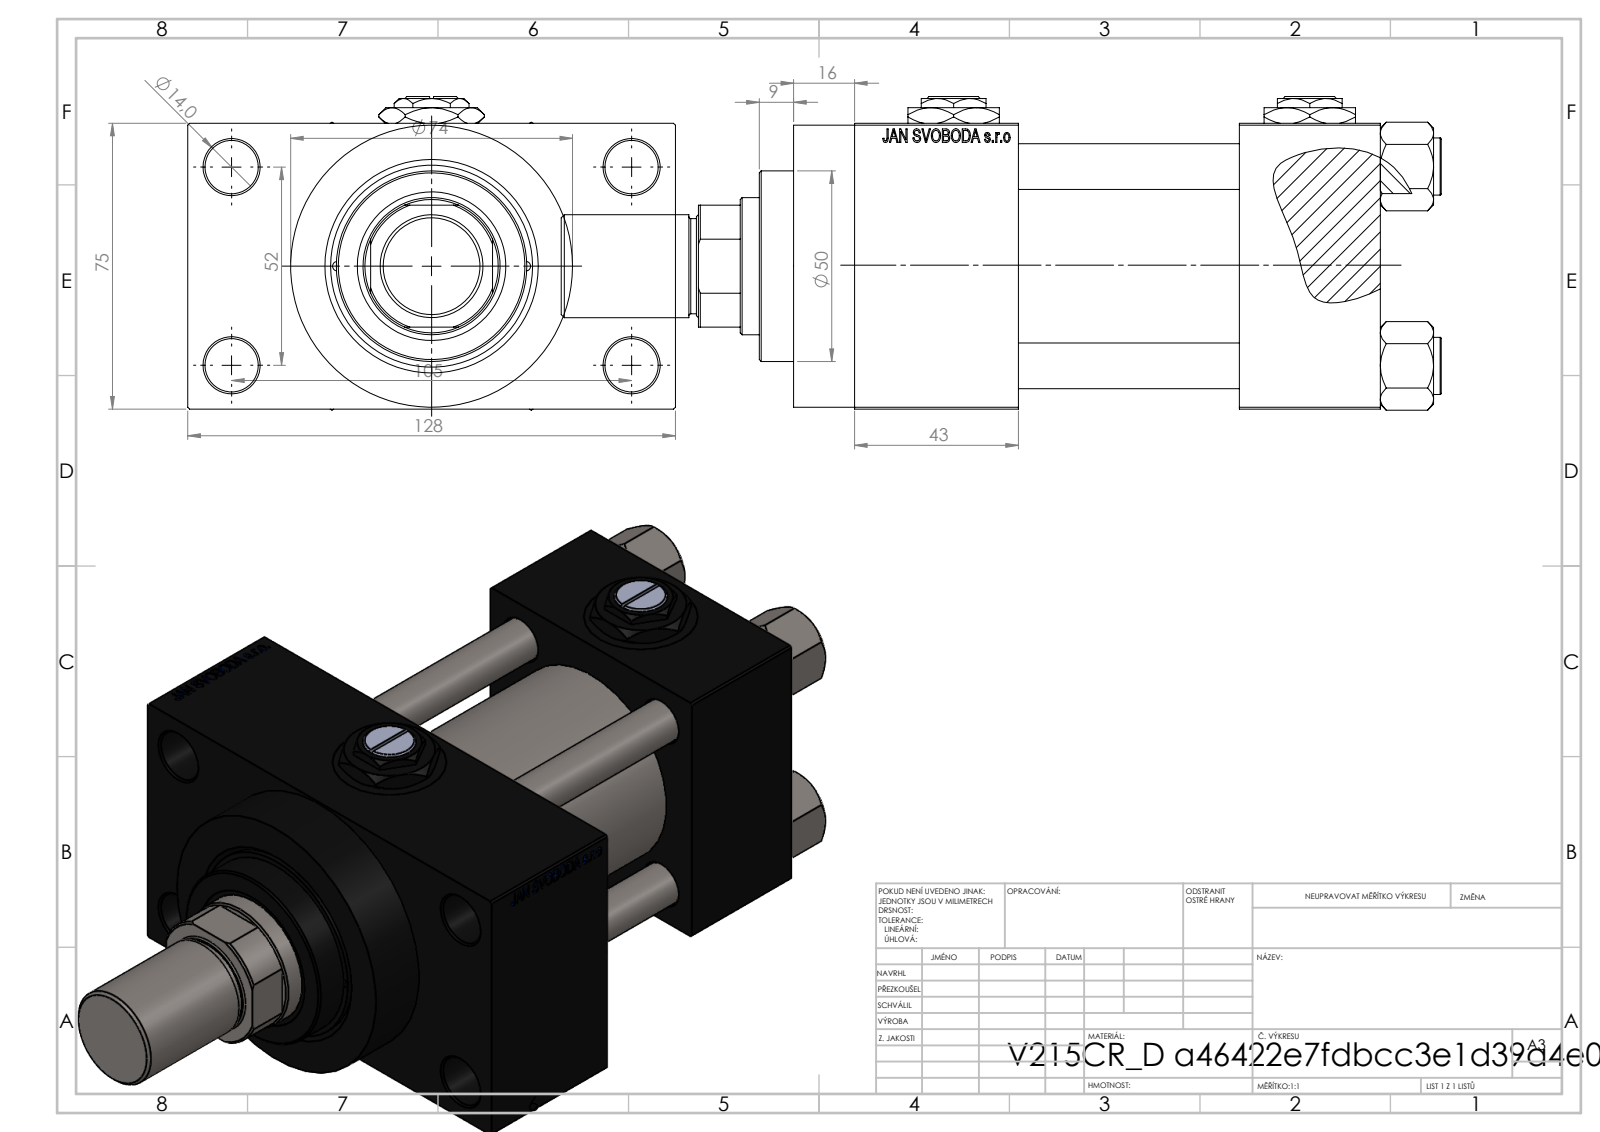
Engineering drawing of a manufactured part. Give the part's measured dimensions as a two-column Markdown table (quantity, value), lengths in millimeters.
| quantity | value |
| --- | --- |
| part name | V215CR_D_TYCINKA; Zatka_pro_OIL_PORT; V215_VC_A; V215CR_D_Body (+3 more) |
| STEP written by | SolidWorks 2019 (CONFIG_CONTROL_DESIGN) |
| units | millimeters |
| bodies | 14 solids, 1228 faces (553 planar, 107 cylindrical, 568 other) |
| overall size | 231 × 128 × 82.27 |
| volume | 833 102 mm³ |
| surface area | 183 980 mm² |
| round holes (diameter × count) | 12 × 4, 14 × 4, 20.96 × 4, 30 × 4, 7 × 3, 2.5 × 2, 25.5 × 1, 36 × 1, 39 × 1, 41 × 1, 53 × 1 |
| round bosses / shafts (diameter × count) | 15 × 4, 74 × 1, 56 × 1, 50 × 1, 27 × 1, 25 × 1 |
| partial cylindrical surfaces (radius × count) | 17.5 × 1 |
| main face-to-face distances | 75, 58, 37, 95, 26.5, 138, 43, 101, 101.5, 16 |
| hole center spacings | 26.19, 26.35, 36.98, 38.03, 52.3, 57.22, 58.43, 58.59 |
